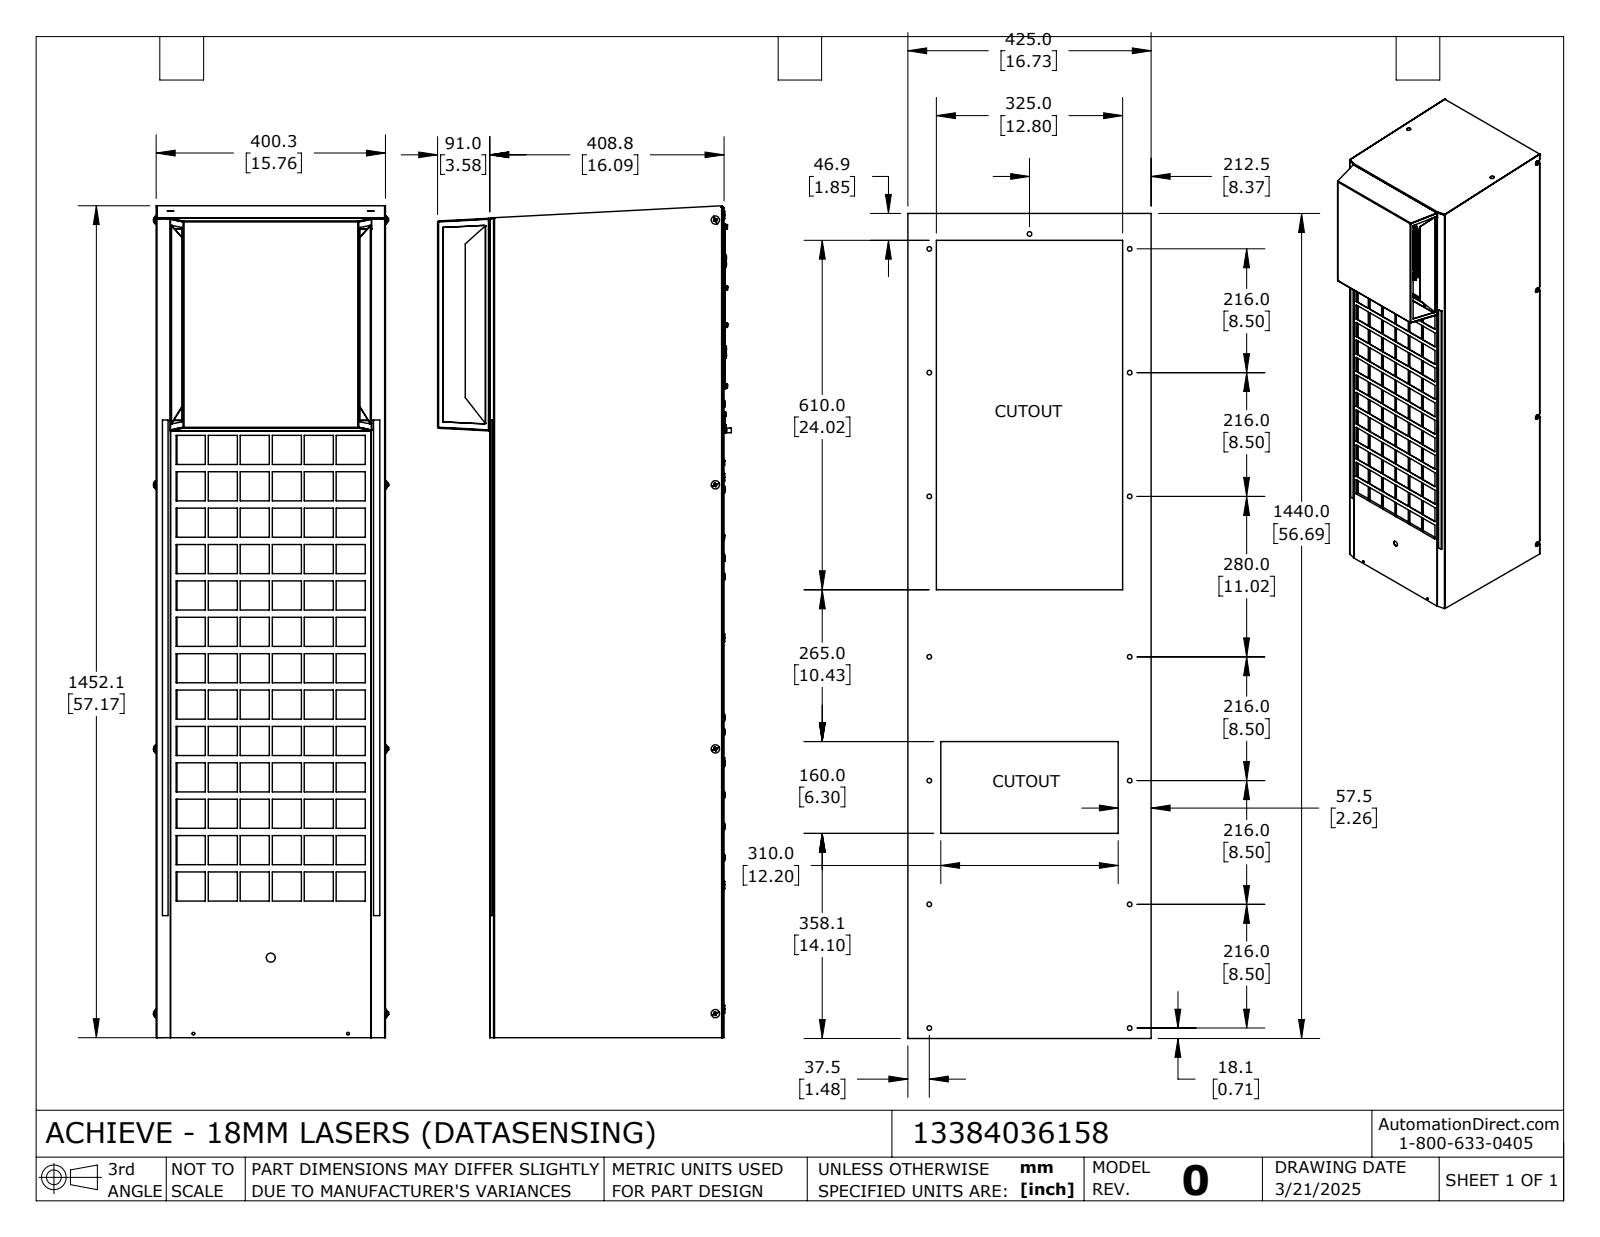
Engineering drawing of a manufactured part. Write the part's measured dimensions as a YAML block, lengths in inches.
part_name: "13384036158_Default"
step_written_by: "SolidWorks 2024 (CONFIG_CONTROL_DESIGN)"
units: inches
bodies: {solids: 1, faces: 6463, planar: 3532, cylindrical: 1827, other: 1104}
overall_size: [57.171, 20.19, 16.113]
volume: 13374
surface_area: 11995
round_holes:
  - {diameter: 0.107, count: 48}
  - {diameter: 0.165, count: 47}
  - {diameter: 0.283, count: 18}
  - {diameter: 0.189, count: 14}
  - {diameter: 0.098, count: 4}
  - {diameter: 0.161, count: 4}
  - {diameter: 0.374, count: 4}
  - {diameter: 0.125, count: 2}
  - {diameter: 0.276, count: 2}
  - {diameter: 0.472, count: 2}
  - {diameter: 0.945, count: 2}
  - {diameter: 0.122, count: 1}
round_bosses_or_shafts:
  - {diameter: 0.178, count: 35}
  - {diameter: 0.512, count: 18}
  - {diameter: 0.315, count: 12}
  - {diameter: 0.157, count: 12}
  - {diameter: 0.122, count: 12}
  - {diameter: 0.354, count: 6}
  - {diameter: 0.079, count: 5}
  - {diameter: 0.573, count: 4}
partial_cylinders:
  - {radius: 0.125, count: 352}
  - {radius: 0.031, count: 43}
  - {radius: 0.076, count: 28}
  - {radius: 0.198, count: 18}
  - {radius: 0.087, count: 13}
  - {radius: 0.132, count: 6}
  - {radius: 0.083, count: 5}
  - {radius: 0.118, count: 5}
face_to_face_distances: [0.045, 0.045, 0.056, 15.714, 15.759, 15.669, 15.715, 0.28, 0.235, 15.435]
hole_center_spacings: [7.48, 14.961, 22.441, 3.028, 0.022, 0.037, 7.874, 29.921]
